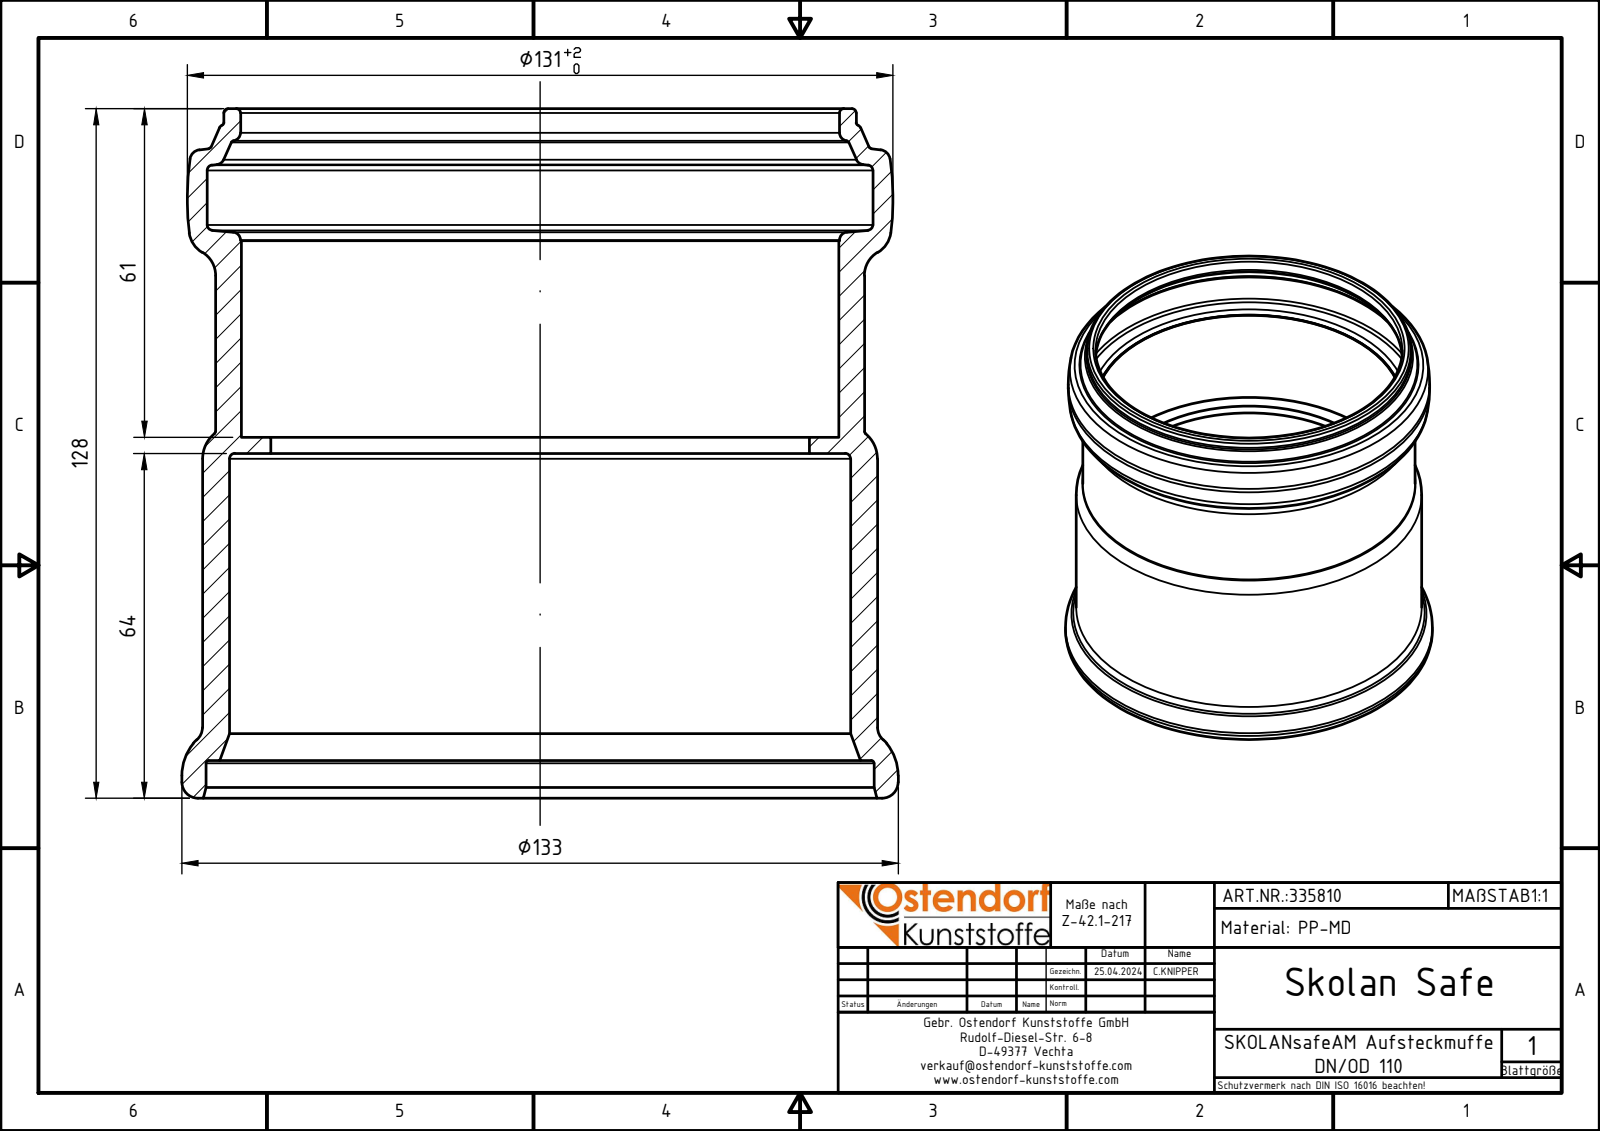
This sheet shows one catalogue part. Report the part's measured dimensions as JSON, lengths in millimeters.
{"part_name": "335810z", "step_written_by": "Autodesk Inventor 2024 (AUTOMOTIVE_DESIGN)", "units": "millimeters", "bodies": {"solids": 1, "faces": 49, "planar": 6, "cylindrical": 12, "other": 31}, "overall_size": [133, 133, 128], "volume_mm3": 243015, "surface_area_mm2": 109398, "round_holes": [[100, 1], [110.9, 1], [111.2, 1], [115.3, 1], [123.6, 1], [124, 1]], "round_bosses_or_shafts": [[133, 1], [131, 1], [125.3, 1], [120.5, 1], [117.4, 1]], "face_to_face_distances": [3, 64, 57, 60, 121, 61, 7, 67, 128, 103.5]}
